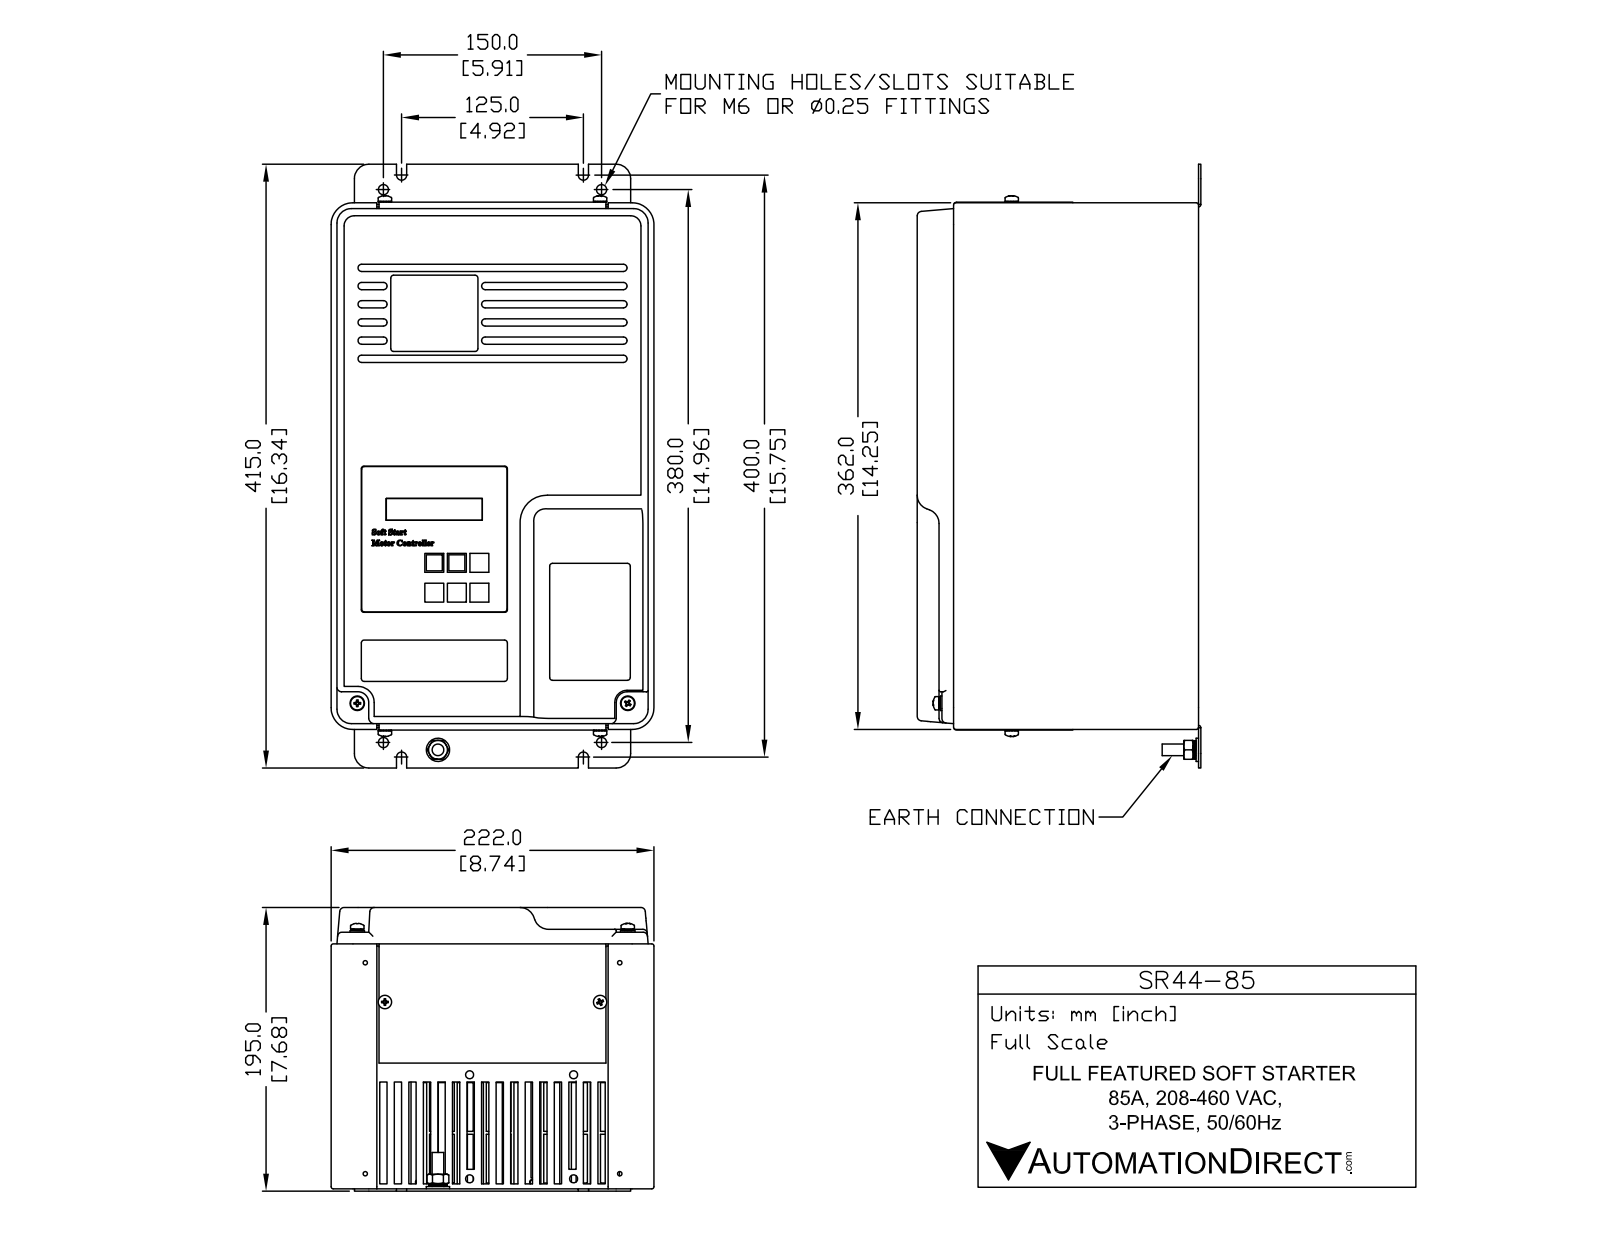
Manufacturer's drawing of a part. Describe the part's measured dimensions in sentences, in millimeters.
The part is named "SR44-85". Its 3-D file was written by "SolidWorks 2013 (AUTOMOTIVE_DESIGN)". It is 1 solid with 768 faces: 455 planar, 175 cylindrical and 138 other. Overall it measures 415 by 222 by 194.7 millimeters. Its volume is 8 231 000 cubic millimeters and its surface area 711 054 square millimeters. Round holes: 4 of diameter 7. Round bosses or shafts: 4 of diameter 10, 1 of diameter 16, 1 of diameter 8. Partial cylindrical surfaces (rounded edges, fillets, slot ends): 30 of radius 2.5, 28 of radius 2.4, 12 of radius 2.49, 11 of radius 1.5, 8 of radius 3, 8 of radius 10, 6 of radius 2, 4 of radius 3.5. The main face-to-face distances are 10.19, 20.38, 30.57, 40.76, 50.95, 61.14, 71.33, 5.9, 81.52, 216.1. The hole center spacings are 150, 380, 408.53.
